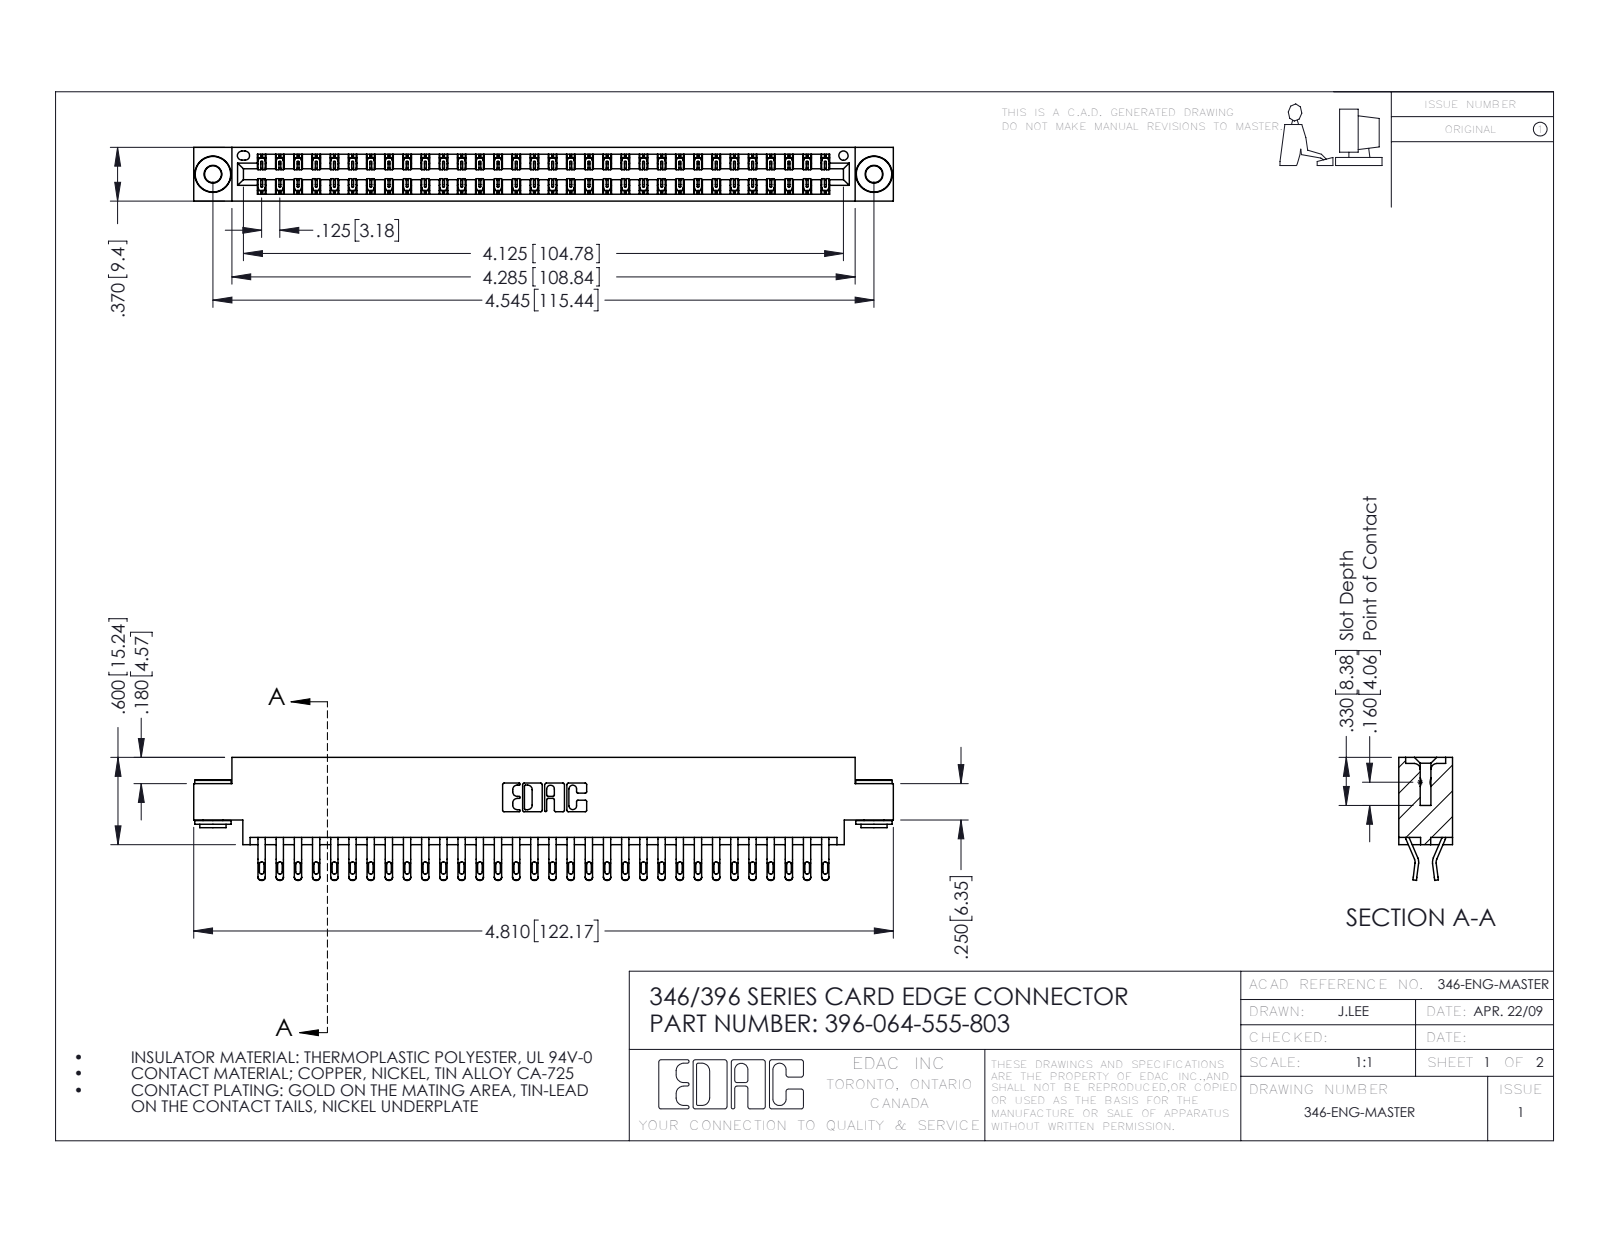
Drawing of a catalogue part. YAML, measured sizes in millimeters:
part_name: "346 Part_0.170 Offset - 0.156 Dia-TH; 345-250-002_345-250-002-102; 345-292-001_555 Tail; 396-064-555-803"
step_written_by: "SolidWorks 2016 (CONFIG_CONTROL_DESIGN)"
units: millimeters
bodies: {solids: 67, faces: 3876, planar: 2202, cylindrical: 1666, other: 8}
overall_size: [122.2, 21.5, 9.4]
volume: 11900
surface_area: 17240
round_holes:
  - {diameter: 2.9, count: 2}
  - {diameter: 4, count: 2}
  - {diameter: 1.6, count: 1}
round_bosses_or_shafts:
  - {diameter: 6.4, count: 2}
  - {diameter: 4.6, count: 2}
  - {diameter: 3.5, count: 2}
partial_cylinders:
  - {radius: 0.4, count: 128}
  - {radius: 0.5, count: 128}
  - {radius: 0.2, count: 96}
  - {radius: 0.3, count: 22}
  - {radius: 0.2, count: 6}
  - {radius: 0.8, count: 6}
  - {radius: 0.7, count: 3}
  - {radius: 0.3, count: 2}
face_to_face_distances: [1.2, 8.2, 9.4, 6.4, 0.6, 7, 1.8, 7.6, 3.8, 5.6]
hole_center_spacings: [6.2, 110.2, 115.4]
